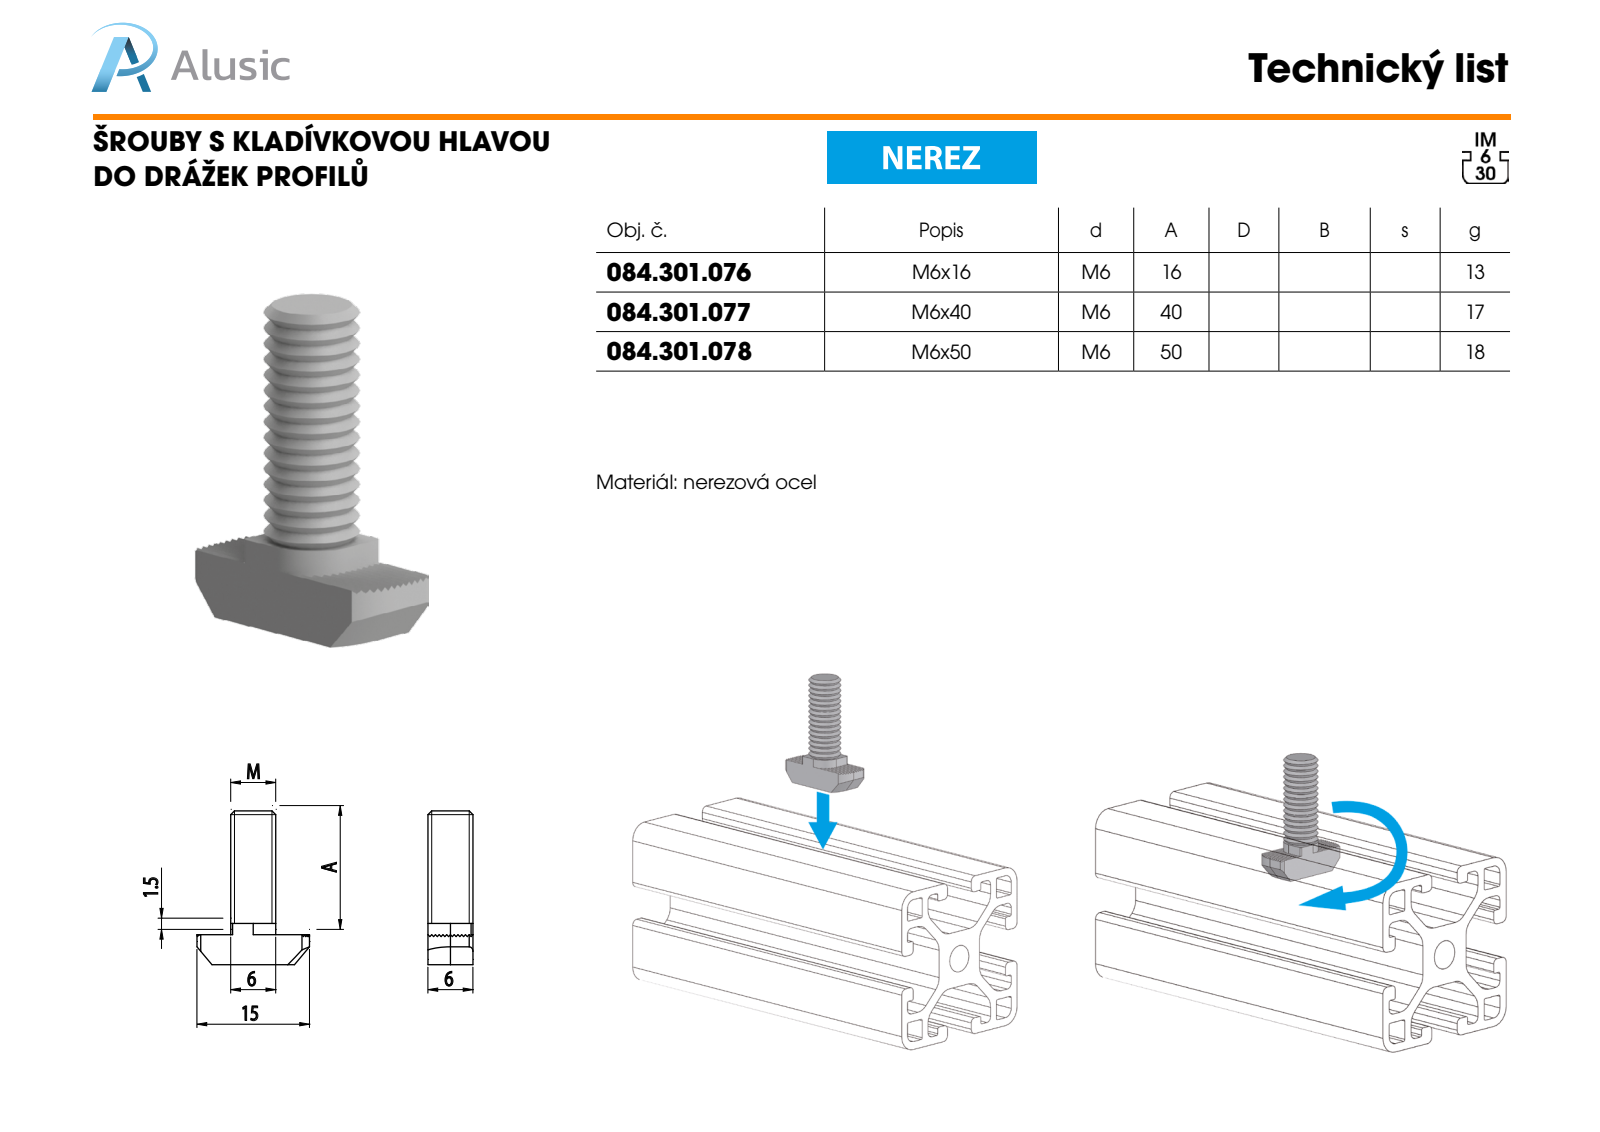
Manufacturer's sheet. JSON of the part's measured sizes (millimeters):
{"part_name": "084.301.077", "step_written_by": "SolidWorks 2016 (CONFIG_CONTROL_DESIGN)", "units": "millimeters", "bodies": {"solids": 1, "faces": 142, "planar": 83, "cylindrical": 56, "other": 3}, "overall_size": [45, 15, 6], "volume_mm3": 1394, "surface_area_mm2": 1335, "round_bosses_or_shafts": [[6, 1]], "partial_cylinders_radius": [[0.3, 2], [5, 2]], "face_to_face_distances": [6, 0.71, 0.36, 1.77, 0.35, 1.06, 1.42, 2.13, 45, 1.07]}
